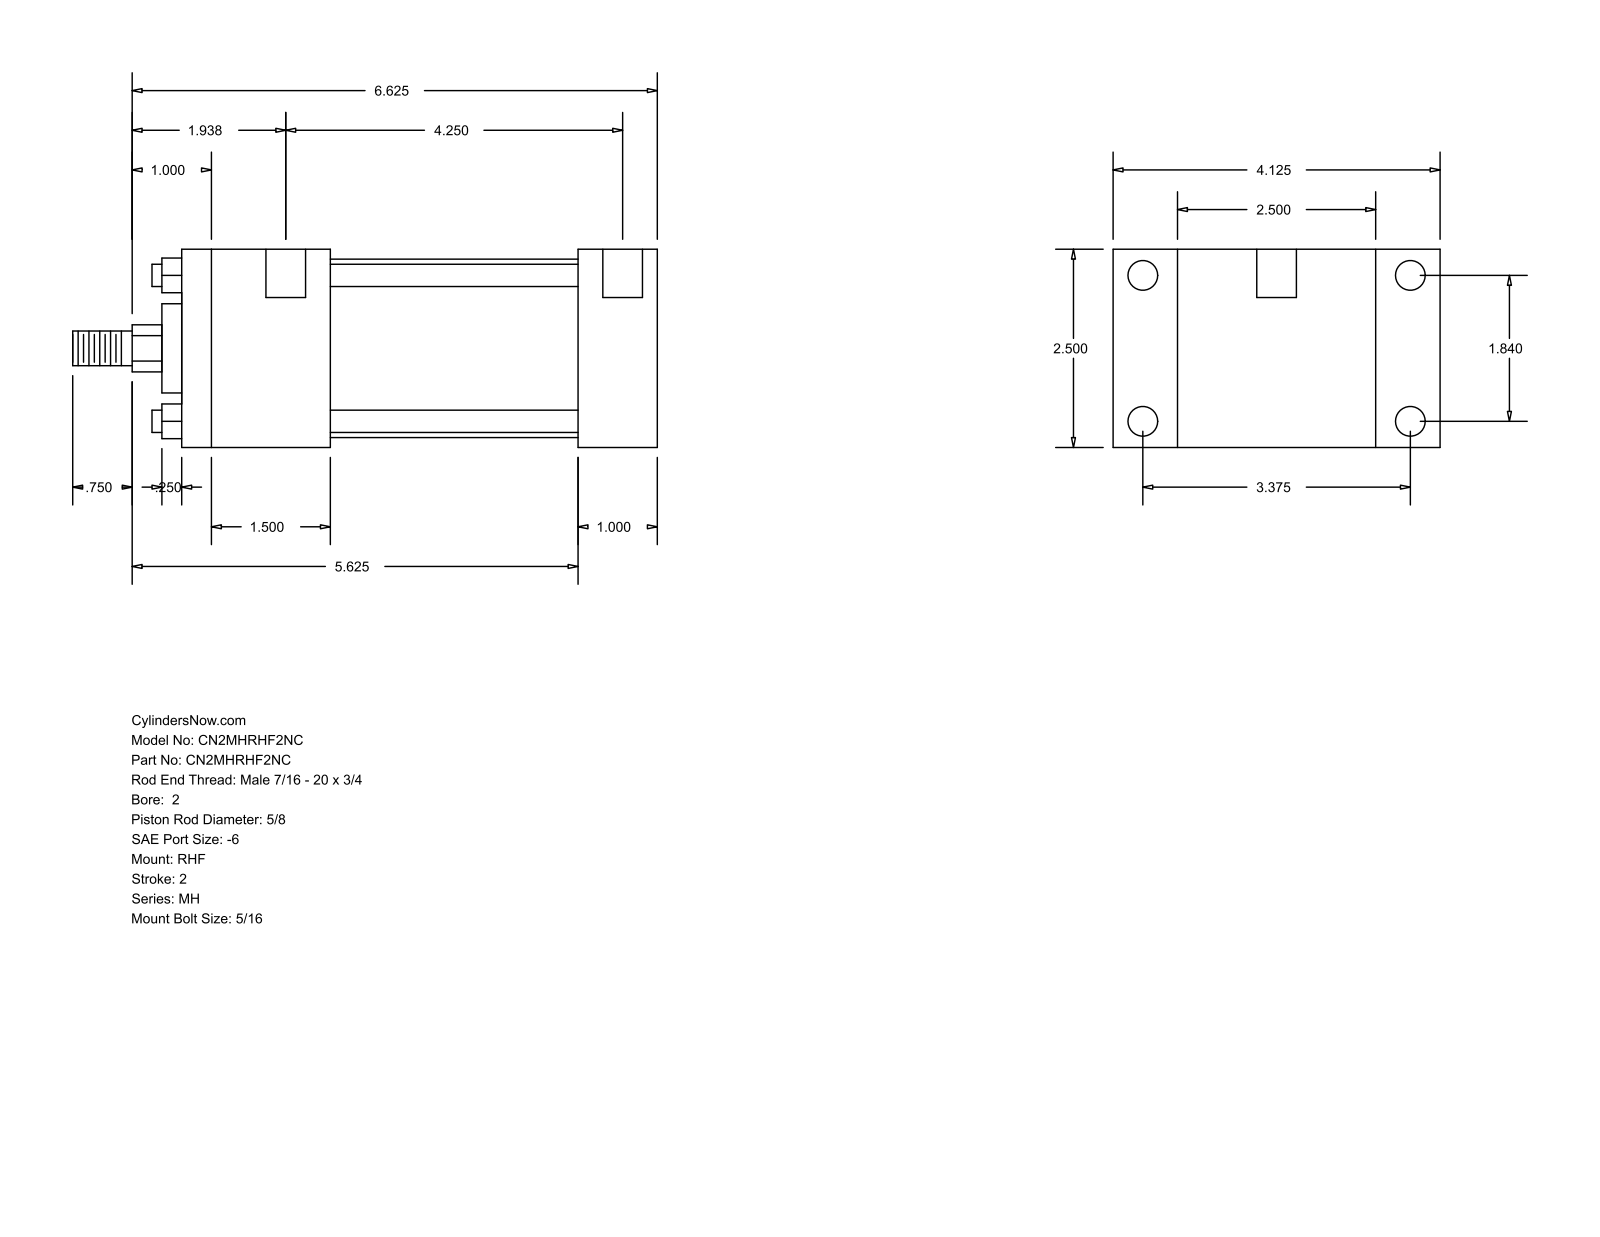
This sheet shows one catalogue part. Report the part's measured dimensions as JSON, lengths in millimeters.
{"part_name": "MH_RHF__0200_0.625", "step_written_by": "GSSL Pune (CONFIG_CONTROL_DESIGN)", "units": "millimeters", "bodies": {"solids": 0, "faces": 88, "planar": 60, "cylindrical": 28, "other": 0}, "overall_size": [187.32, 104.78, 63.5], "round_holes": [[5.56, 4], [9.53, 4], [12.7, 2]], "round_bosses_or_shafts": [[7.14, 4], [57.15, 1], [28.57, 1], [15.88, 1], [11.11, 1]], "partial_cylinders_radius": [[7.54, 1]], "face_to_face_distances": [63.5, 25.4, 20.64, 84.14, 127, 152.4, 104.78, 47.62, 79.38, 6.35], "hole_center_spacings": [46.74, 85.72, 97.63, 115.89, 3.18, 4.76, 107.95, 111.13]}
